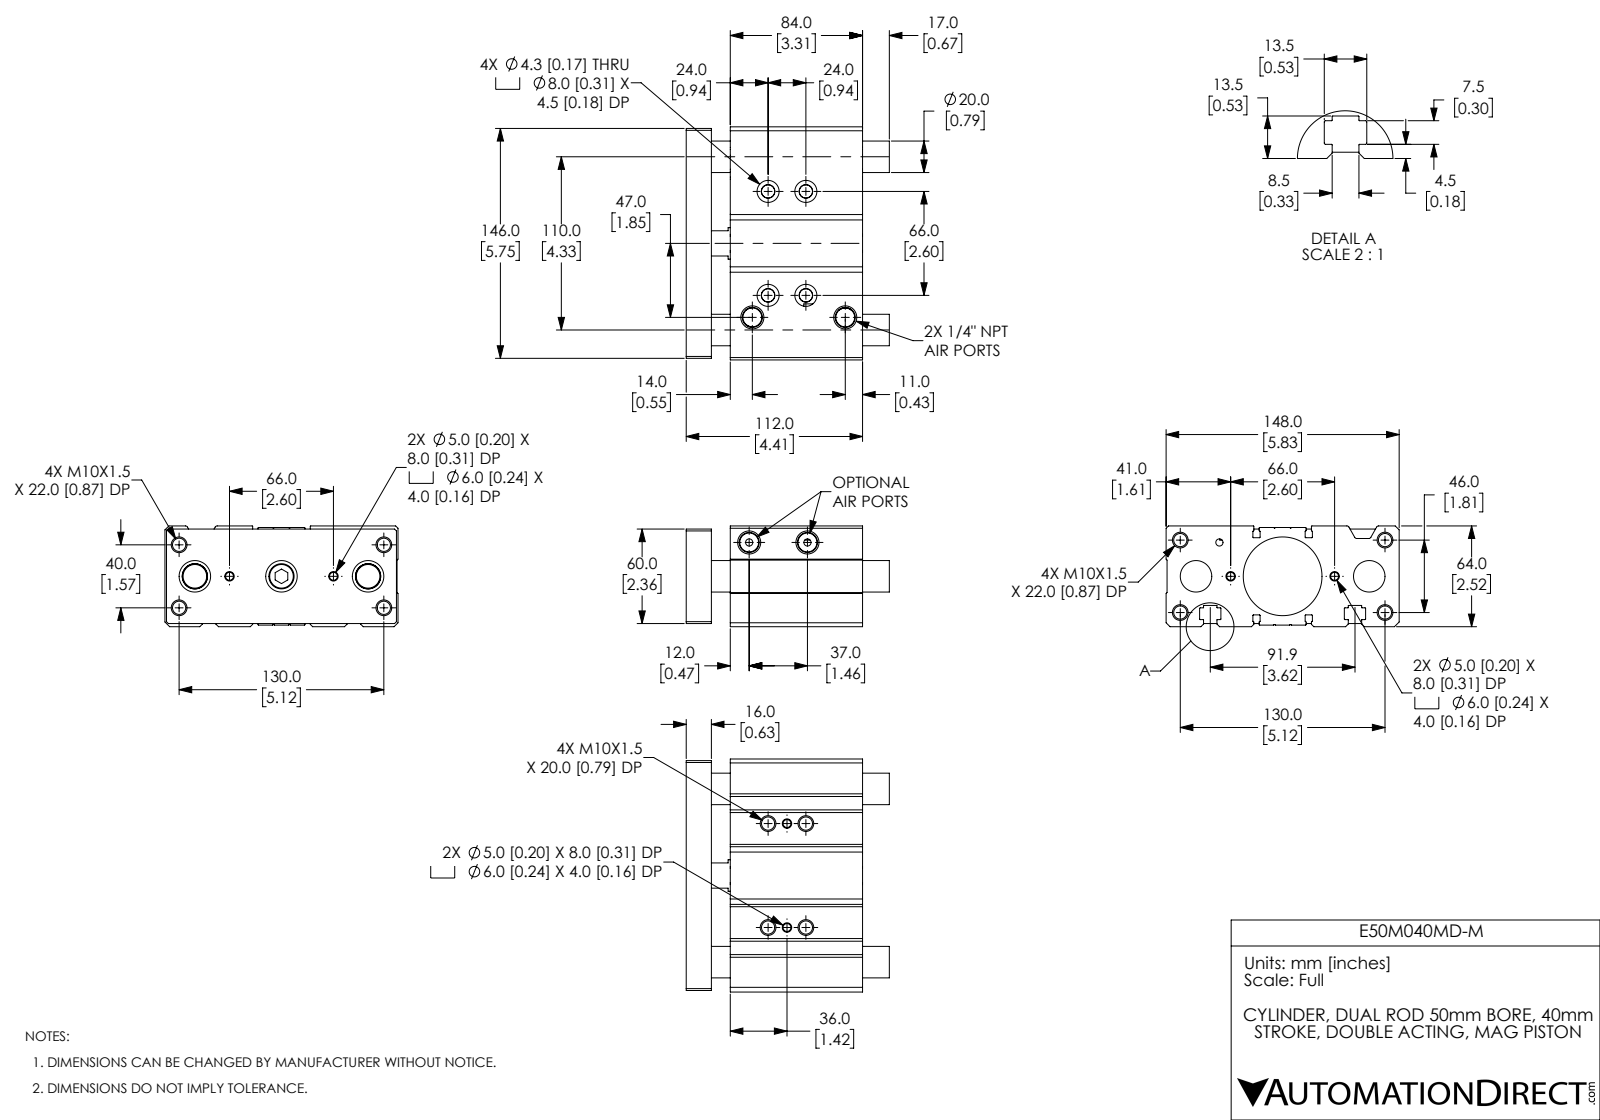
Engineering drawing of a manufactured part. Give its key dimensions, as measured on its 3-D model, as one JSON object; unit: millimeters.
{"part_name": "E50M040MD-M_BODY; E50M040MD-M; E50M040MD-M_ENDPLATE", "step_written_by": "SolidWorks 2019 (CONFIG_CONTROL_DESIGN)", "units": "millimeters", "bodies": {"solids": 5, "faces": 423, "planar": 139, "cylindrical": 190, "other": 94}, "overall_size": [148, 129, 64], "volume_mm3": 797702, "surface_area_mm2": 160420, "round_holes": [[8.38, 12], [5, 4], [6, 4], [8.6, 4], [14, 4], [4.57, 3], [10, 3], [20, 3], [16, 2], [20, 1], [50, 1], [50, 1]], "round_bosses_or_shafts": [[16, 1]], "partial_cylinders_radius": [[0.2, 32], [0.4, 28], [1.5, 4], [0.3, 2]], "face_to_face_distances": [1, 12, 28, 16, 62, 64, 112, 96, 84, 5.5], "hole_center_spacings": [3, 12, 22.36, 25.08, 37.74, 39.41, 43, 66]}
